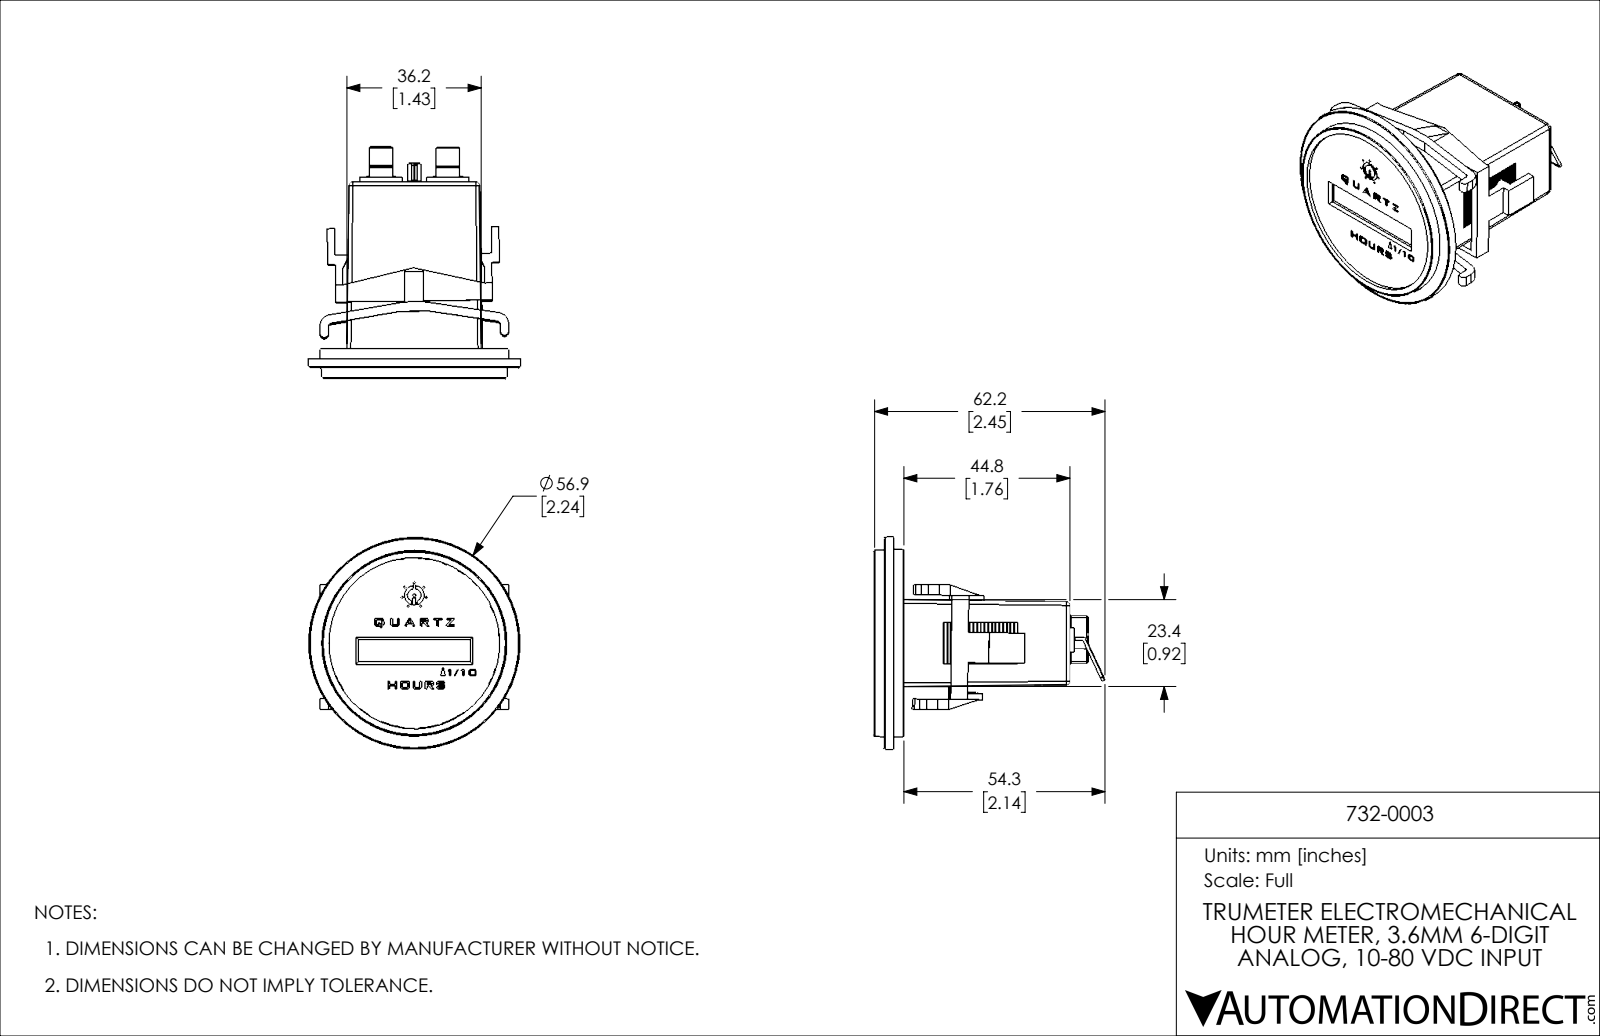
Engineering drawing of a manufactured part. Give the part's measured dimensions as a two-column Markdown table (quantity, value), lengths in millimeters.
| quantity | value |
| --- | --- |
| part name | 732-0003 |
| STEP written by | SolidWorks 2021 (CONFIG_CONTROL_DESIGN) |
| units | millimeters |
| bodies | 1 solid, 847 faces (640 planar, 147 cylindrical, 60 other) |
| overall size | 62.16 × 56.9 × 56.9 |
| volume | 18 935 mm³ |
| surface area | 25 335 mm² |
| round holes (diameter × count) | 0.5 × 7, 1.5 × 4, 0.84 × 1, 5.26 × 1, 46 × 1 |
| round bosses / shafts (diameter × count) | 50.3 × 1, 3.58 × 1 |
| partial cylindrical surfaces (radius × count) | 0.5 × 30, 1 × 17, 0.3 × 15, 1.5 × 6, 0.35 × 4, 0.76 × 4, 1.15 × 4, 1.75 × 4 |
| main face-to-face distances | 1.4, 0.4, 2.5, 2.9, 4.3, 2.4, 1.8, 51.7, 50.3, 49.9 |
| hole center spacings | 3.36, 2.85, 6.5, 5.16, 2.84, 3.37, 5.15, 5.51 |
